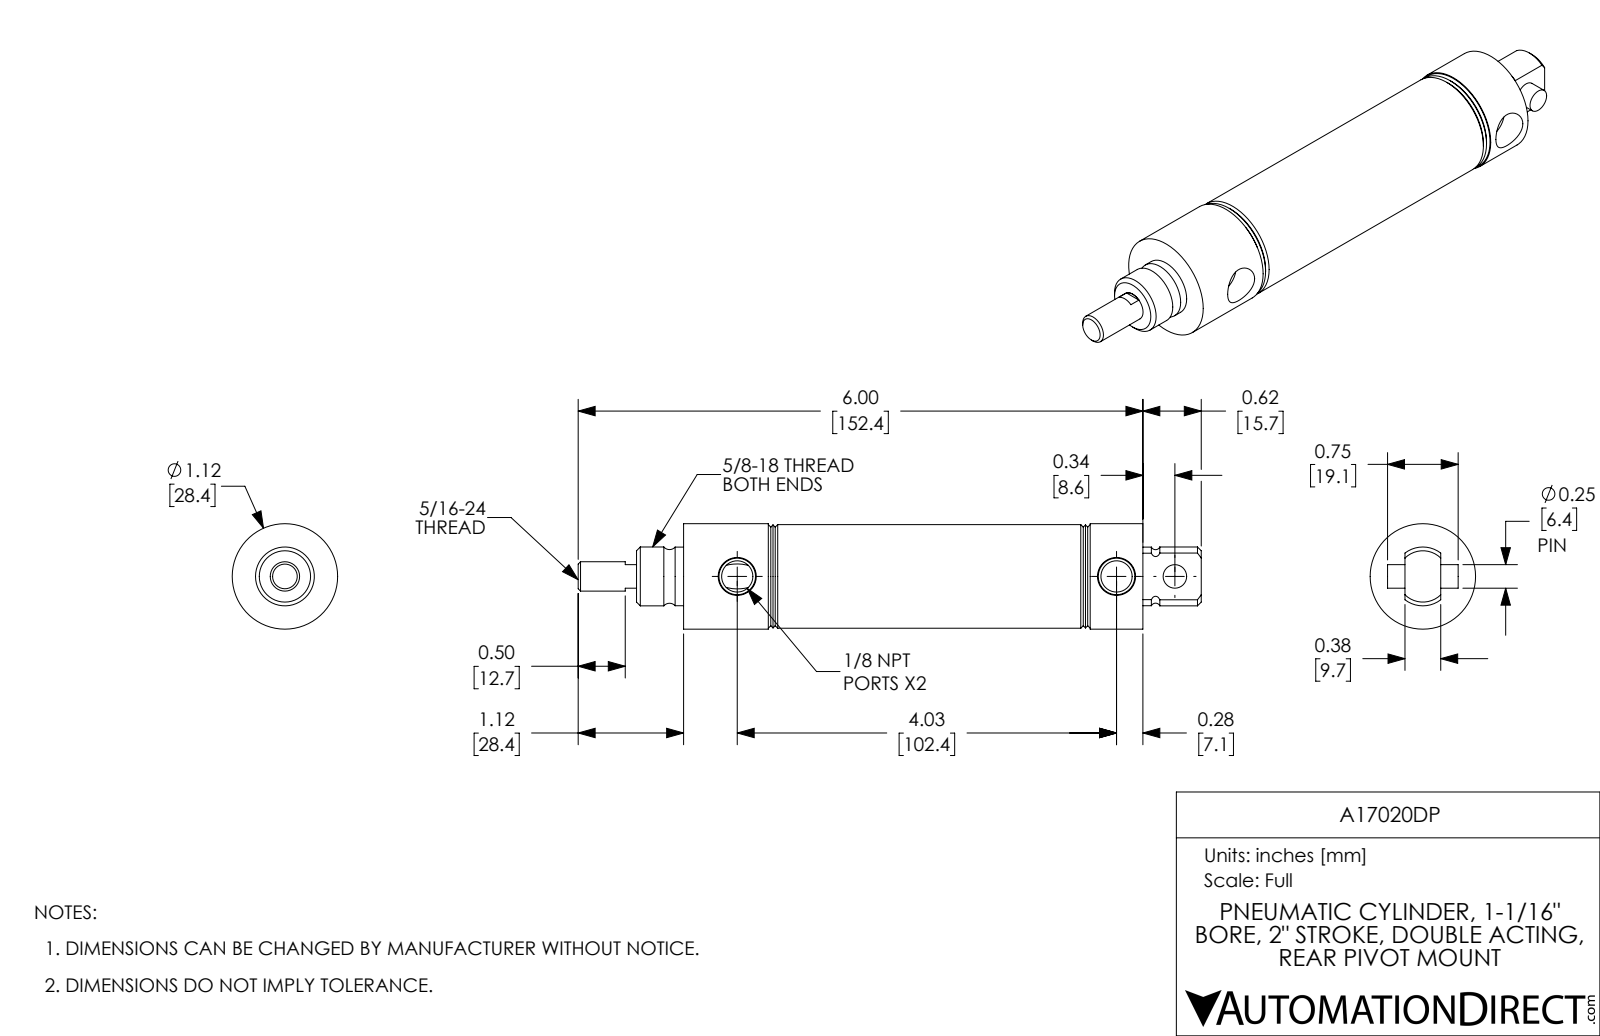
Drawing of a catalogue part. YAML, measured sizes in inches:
part_name: "A17020DP-MainBody; A17020DP-Rod; A17020DP-PIN; A17020DP"
step_written_by: "SolidWorks 2017 (AUTOMOTIVE_DESIGN)"
units: inches
bodies: {solids: 3, faces: 91, planar: 23, cylindrical: 30, other: 38}
overall_size: [6.62, 1.12, 1.12]
volume: 3.308
surface_area: 42.32
round_holes:
  - {diameter: 0.332, count: 2}
  - {diameter: 0.25, count: 1}
  - {diameter: 0.312, count: 1}
  - {diameter: 1.063, count: 1}
round_bosses_or_shafts:
  - {diameter: 1.12, count: 1}
  - {diameter: 1.1, count: 1}
  - {diameter: 0.625, count: 1}
  - {diameter: 0.623, count: 1}
partial_cylinders:
  - {radius: 0.313, count: 1}
face_to_face_distances: [0.5, 3.69, 2.5, 2, 1.19, 1.69, 3.69, 4.88, 3.19, 1.19]
hole_center_spacings: [0.62, 4.03, 4.65]
